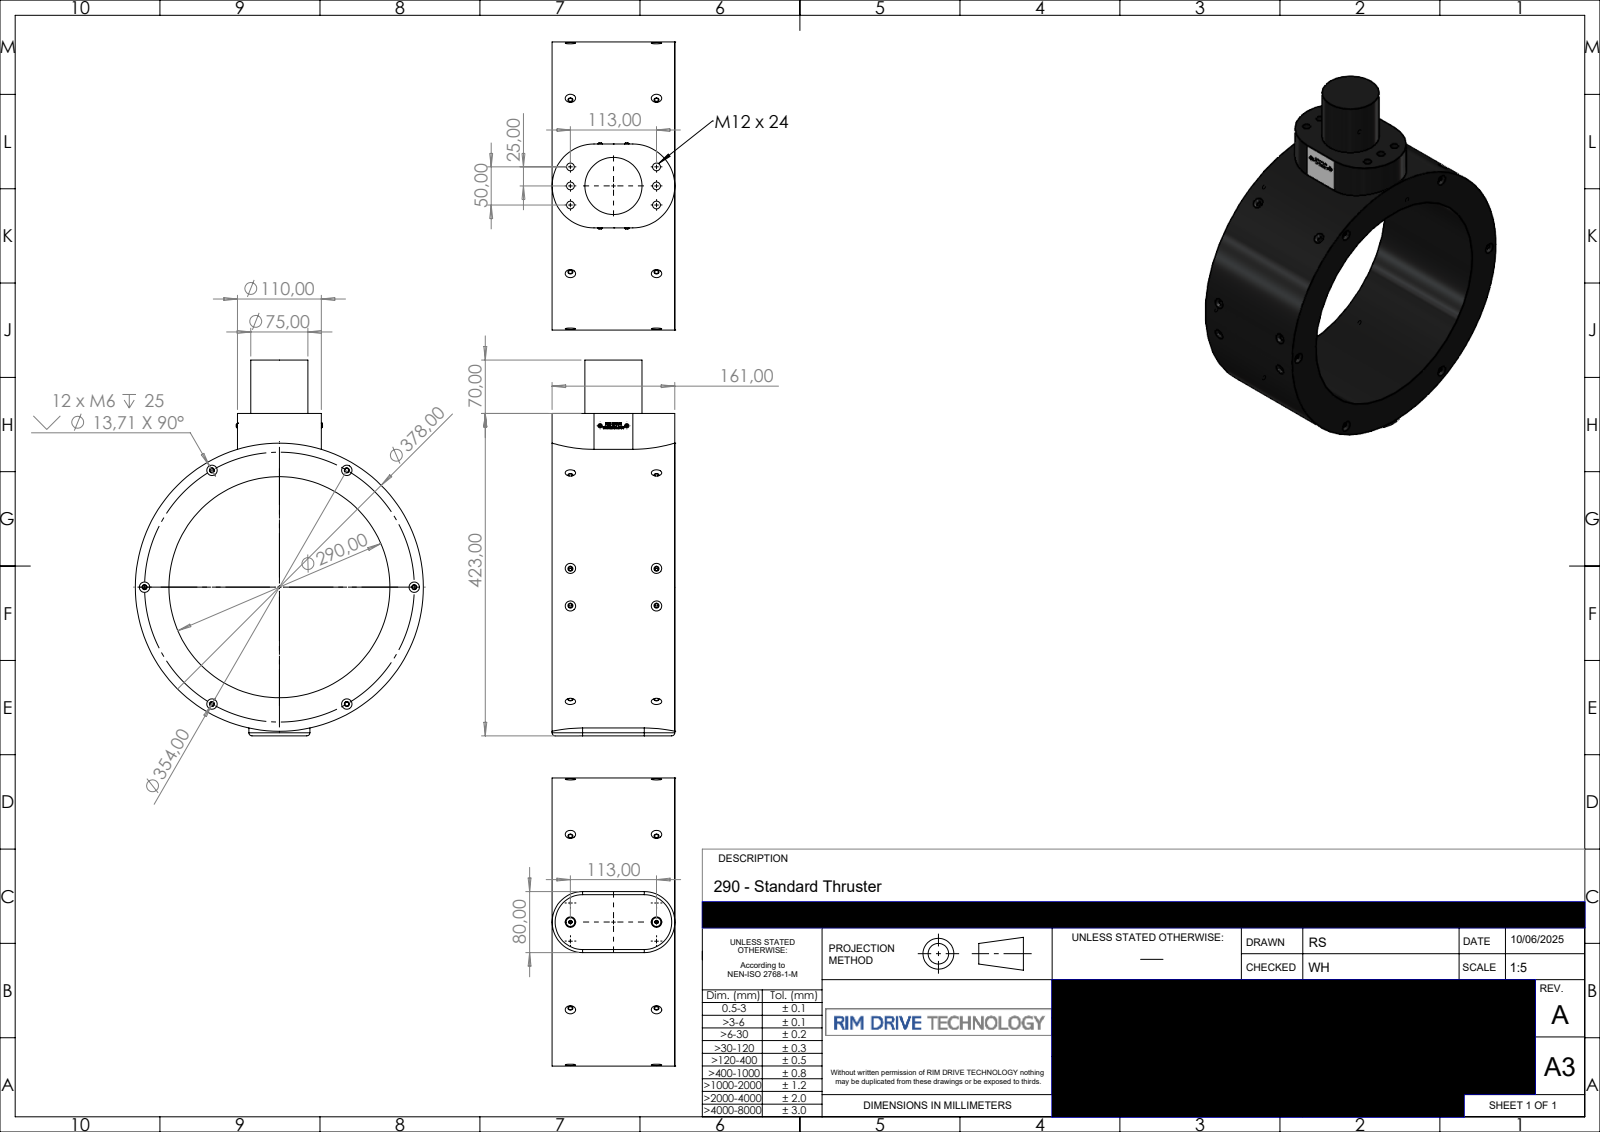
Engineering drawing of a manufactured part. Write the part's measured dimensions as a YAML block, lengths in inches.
part_name: "P-290-030-rev-A-ST"
step_written_by: "SolidWorks 2024 (AUTOMOTIVE_DESIGN)"
units: inches
bodies: {solids: 1, faces: 708, planar: 431, cylindrical: 66, other: 211}
overall_size: [19.409, 14.882, 6.341]
volume: 513.8
surface_area: 749.9
round_holes:
  - {diameter: 0.197, count: 22}
  - {diameter: 0.26, count: 6}
  - {diameter: 0.402, count: 6}
  - {diameter: 0.138, count: 2}
  - {diameter: 11.417, count: 1}
round_bosses_or_shafts:
  - {diameter: 0.456, count: 2}
  - {diameter: 0.224, count: 2}
  - {diameter: 14.882, count: 1}
  - {diameter: 2.953, count: 1}
partial_cylinders:
  - {radius: 0.157, count: 2}
  - {radius: 1.575, count: 2}
  - {radius: 2.165, count: 2}
face_to_face_distances: [6.341, 16.654, 19.409, 2.756, 4.331, 3.74, 0.591, 3.15, 15.669, 0.984]
hole_center_spacings: [4.449, 6.969, 0.014, 0.984, 4.556, 12.07, 1.969, 4.865]
